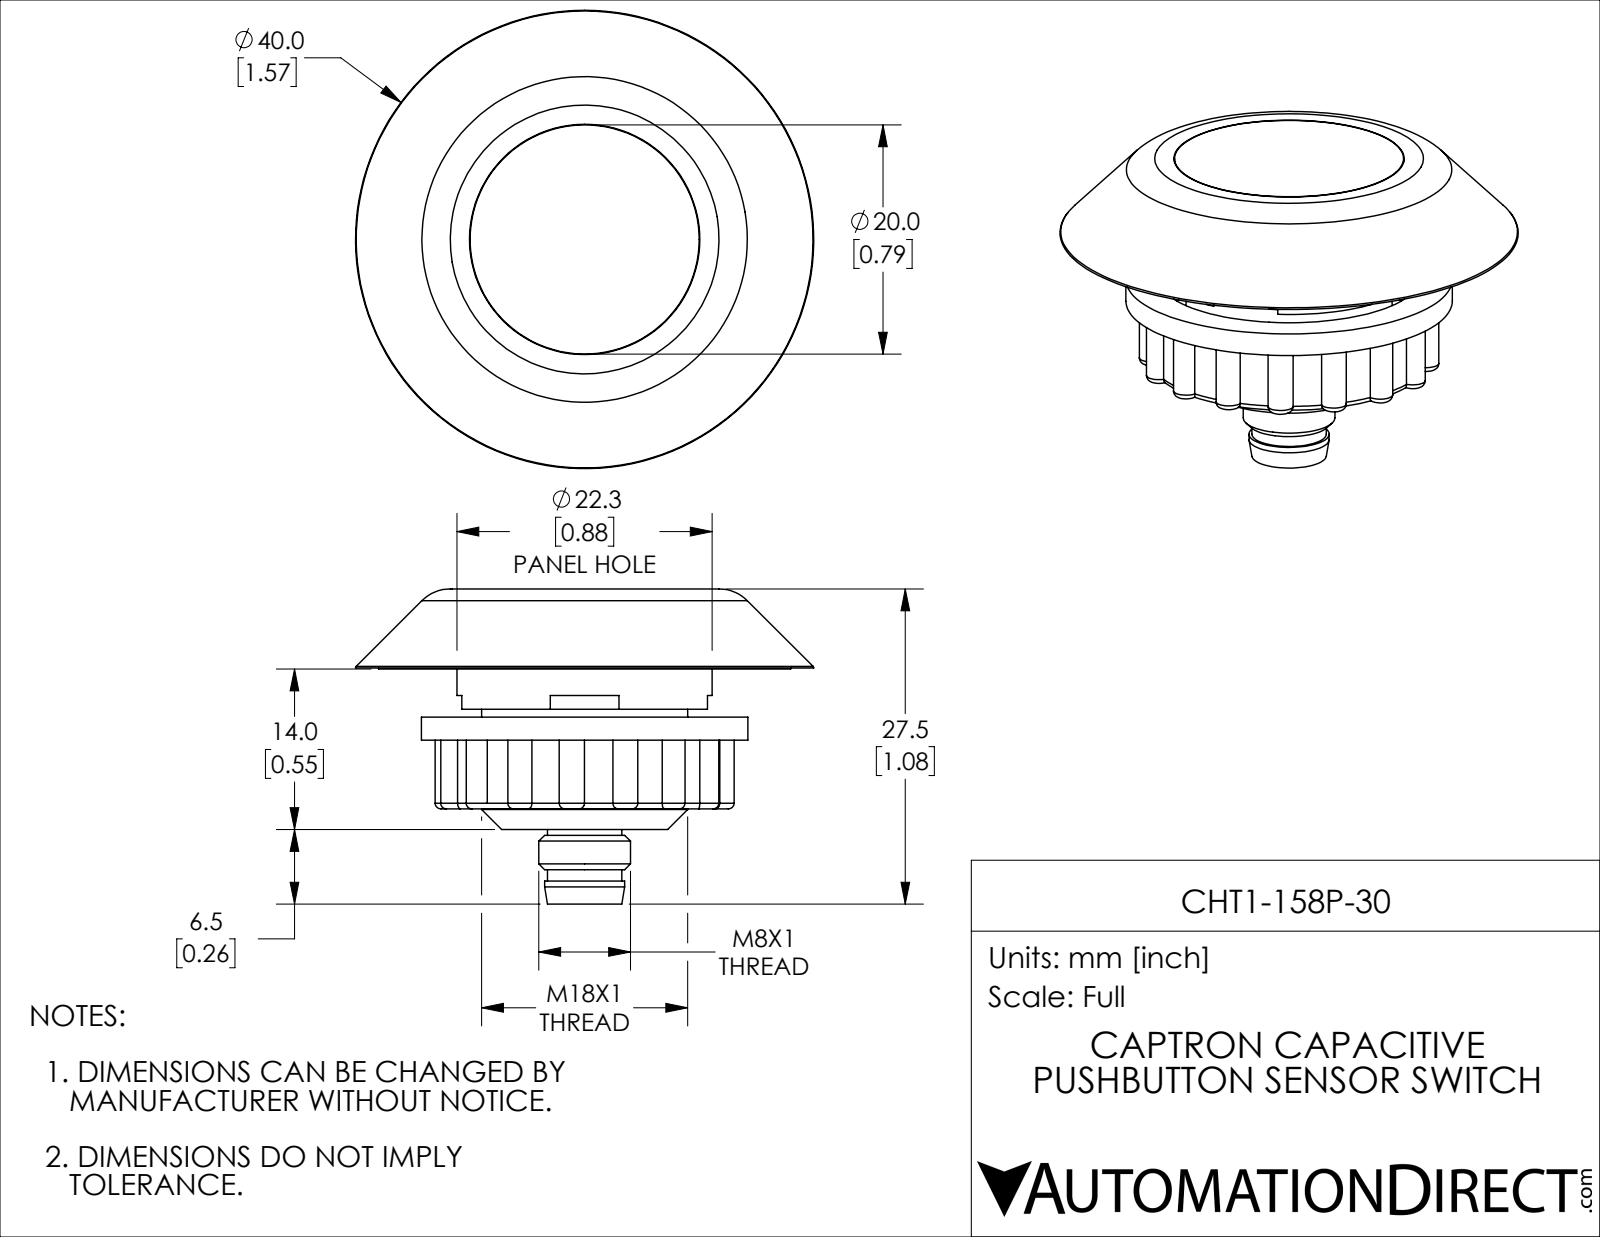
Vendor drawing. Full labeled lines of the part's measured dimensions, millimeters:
Part name (STEP PRODUCT): CHT1-158P-30
STEP written by: SolidWorks 2019 (CONFIG_CONTROL_DESIGN)
Units: millimetres
Bodies: 10 solids, 218 faces (42 planar, 97 cylindrical, 79 other)
Overall size (bounding box): 40 × 40 × 27.5
Volume: 13 140 mm³ · Surface area: 9 399 mm²
Round holes (diameter × count): ⌀2 ×2, ⌀6 ×1, ⌀17 ×1, ⌀20.1 ×1, ⌀22.6 ×1, ⌀23 ×1, ⌀37 ×1
Round bosses / shafts (diameter × count): ⌀1 ×4, ⌀36 ×1, ⌀28.5 ×1, ⌀22.28 ×1, ⌀19.08 ×1, ⌀18 ×1, ⌀8 ×1, ⌀7 ×1
Partial cylindrical surfaces — rounded edges, fillets, slot ends (radius × count): R1.1 ×16, R9.9 ×1, R12 ×1
Main face-to-face distances: 6, 3.5, 3, 1, 4, 7, 0.9, 8.2, 2.5, 2
Hole centre spacings: 5.5, 11
